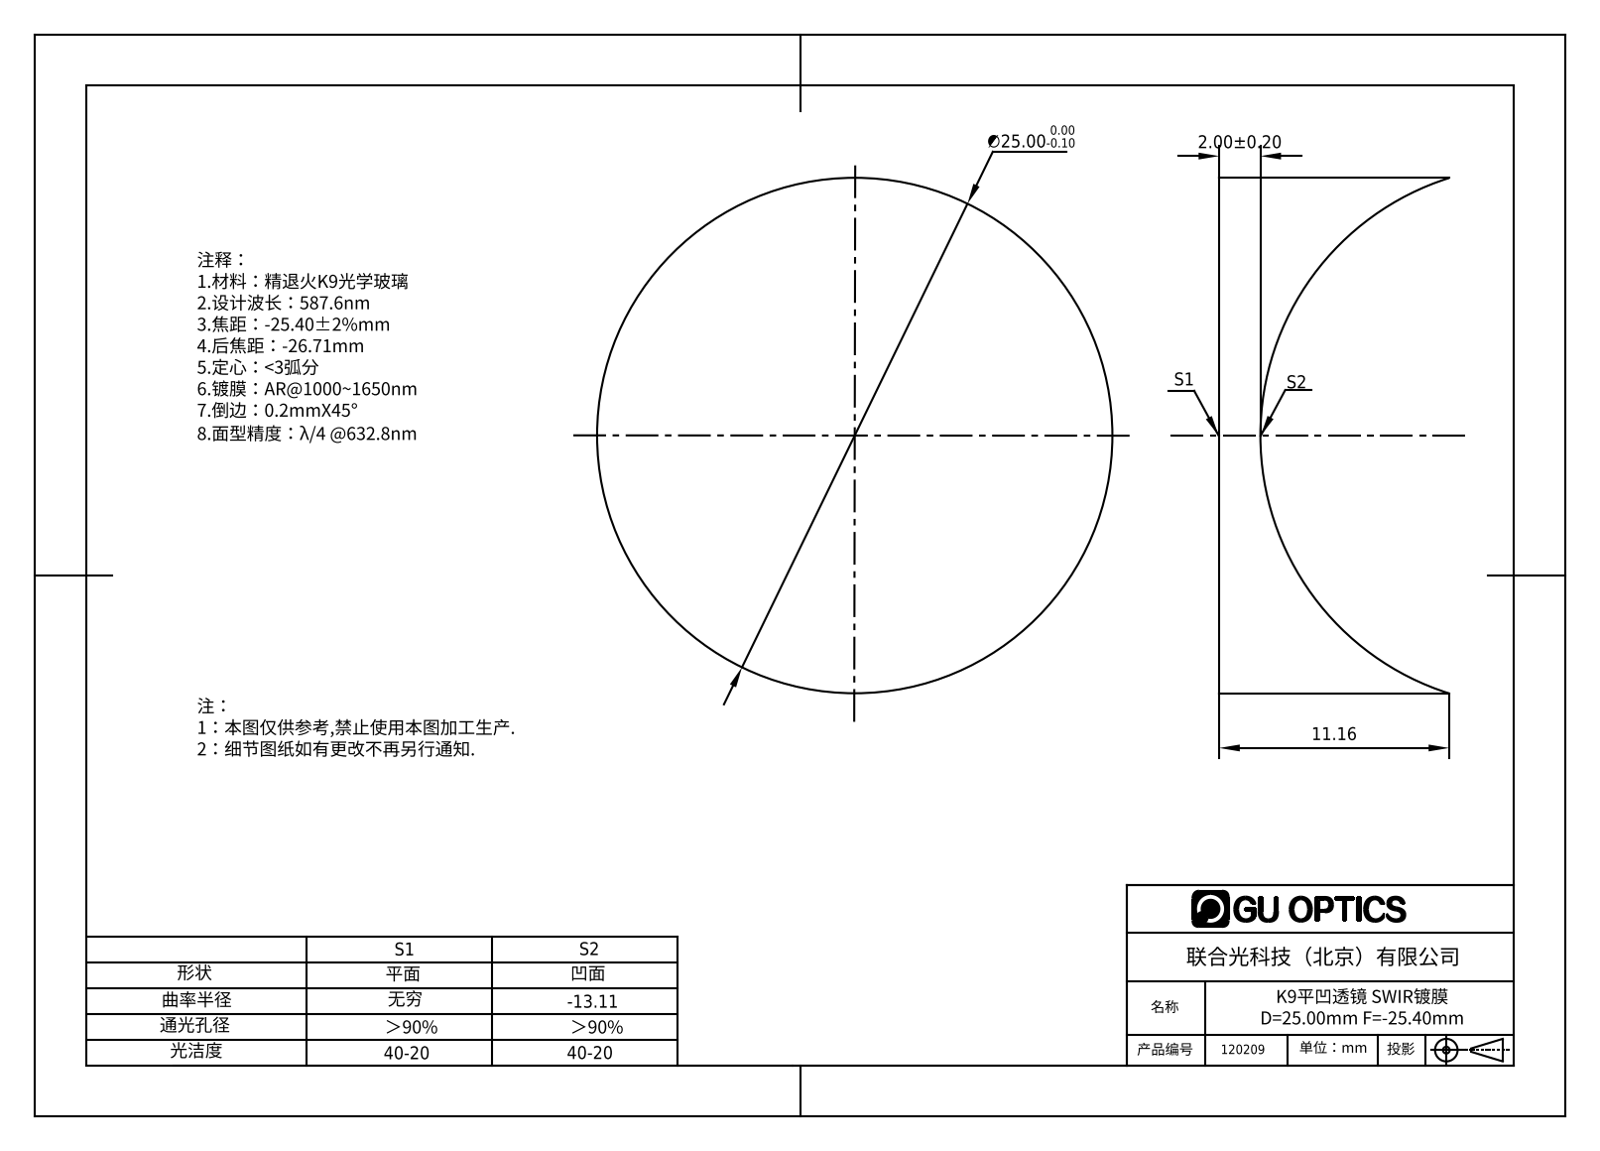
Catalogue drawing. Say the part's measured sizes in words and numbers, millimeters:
The part is named "120149". Its 3-D file was written by "SolidWorks 2016 (AUTOMOTIVE_DESIGN)". It is 1 solid with 5 faces: 1 planar, 2 cylindrical and 2 other. Overall it measures 25 by 25 by 11.16 millimeters. Its volume is 2 828 cubic millimeters and its surface area 2 122 square millimeters. Round bosses or shafts: 1 of diameter 25.
